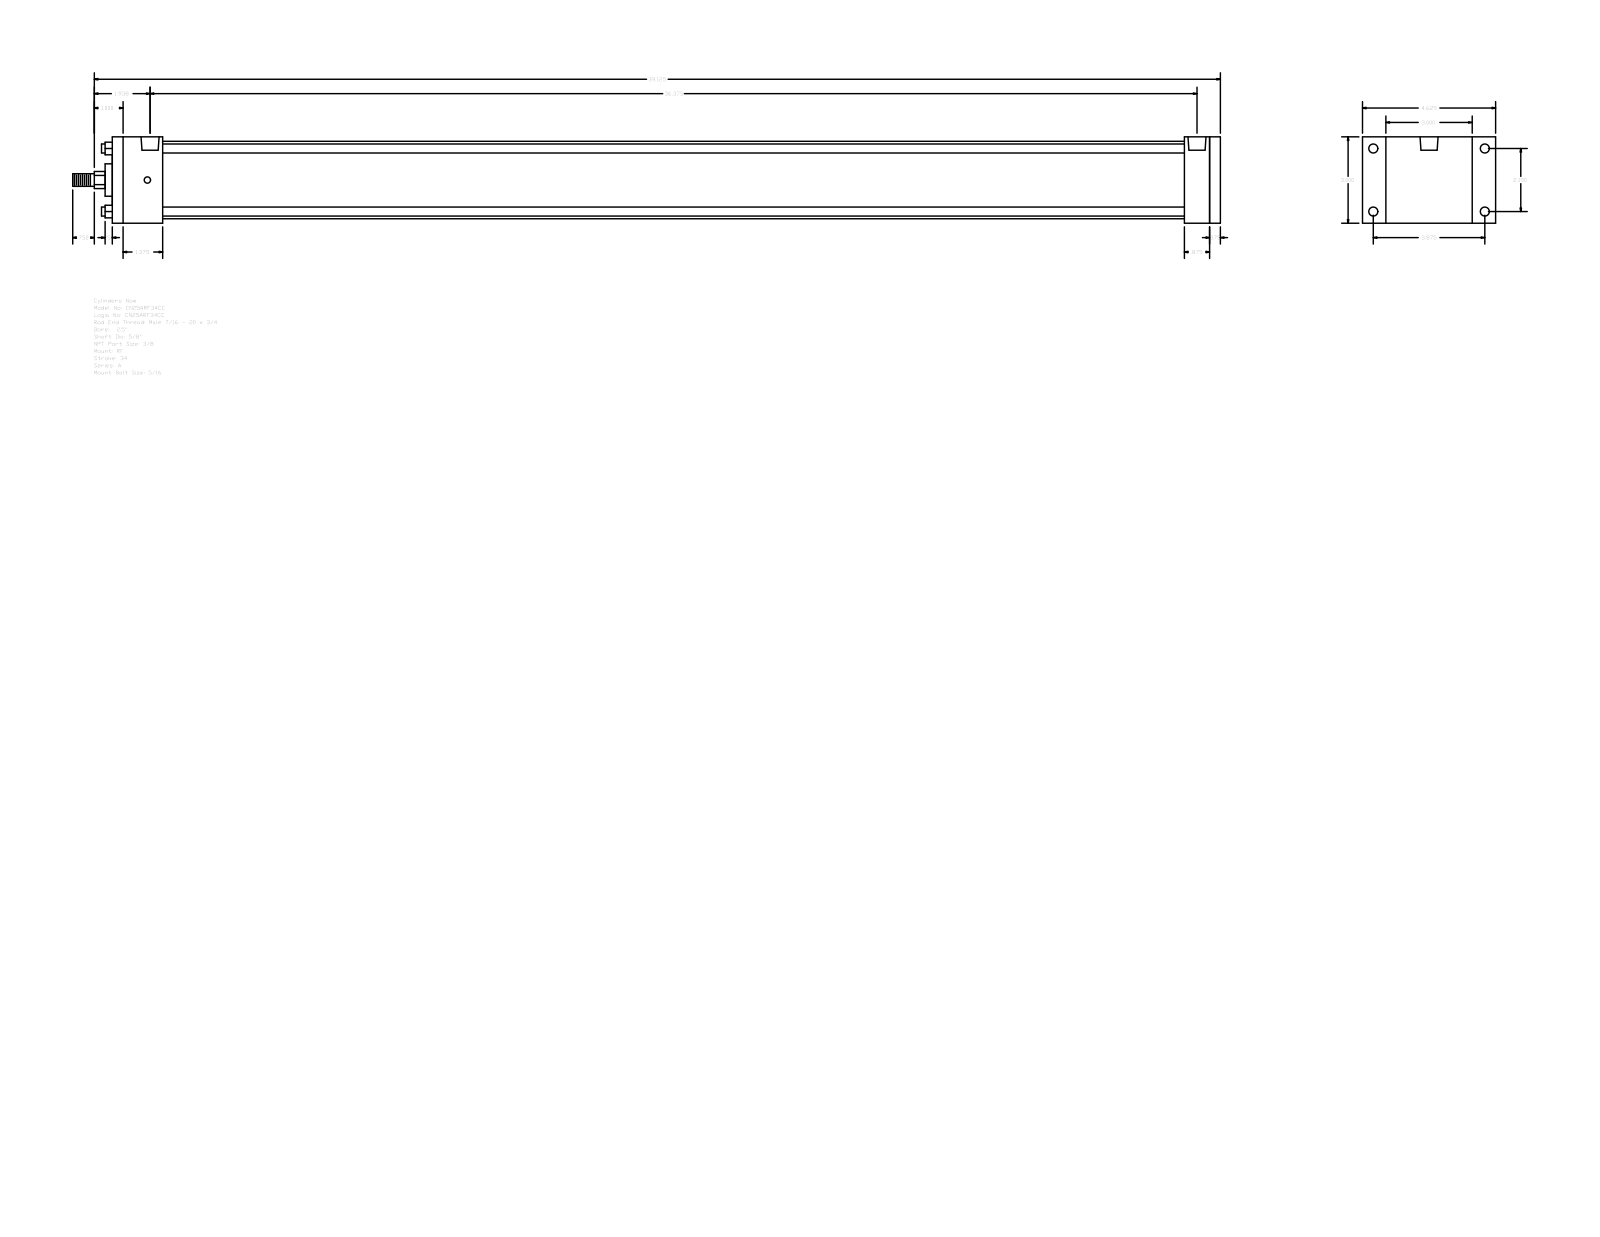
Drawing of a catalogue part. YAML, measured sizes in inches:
part_name: "A_RF__0250_0.625"
step_written_by: "GSSL Pune (CONFIG_CONTROL_DESIGN)"
units: inches
bodies: {solids: 0, faces: 92, planar: 64, cylindrical: 28, other: 0}
overall_size: [39.875, 4.625, 3]
round_holes:
  - {diameter: 0.219, count: 4}
  - {diameter: 0.313, count: 4}
  - {diameter: 0.627, count: 2}
round_bosses_or_shafts:
  - {diameter: 0.313, count: 4}
  - {diameter: 2.69, count: 1}
  - {diameter: 1.125, count: 1}
  - {diameter: 0.625, count: 1}
  - {diameter: 0.437, count: 1}
partial_cylinders:
  - {radius: 0.297, count: 1}
face_to_face_distances: [3, 38.5, 38.125, 0.375, 1.75, 1.25, 37.25, 35.5, 36.375, 36.75]
hole_center_spacings: [0.094, 2.19, 3.875, 4.451, 36.469, 36.563, 36.375]
